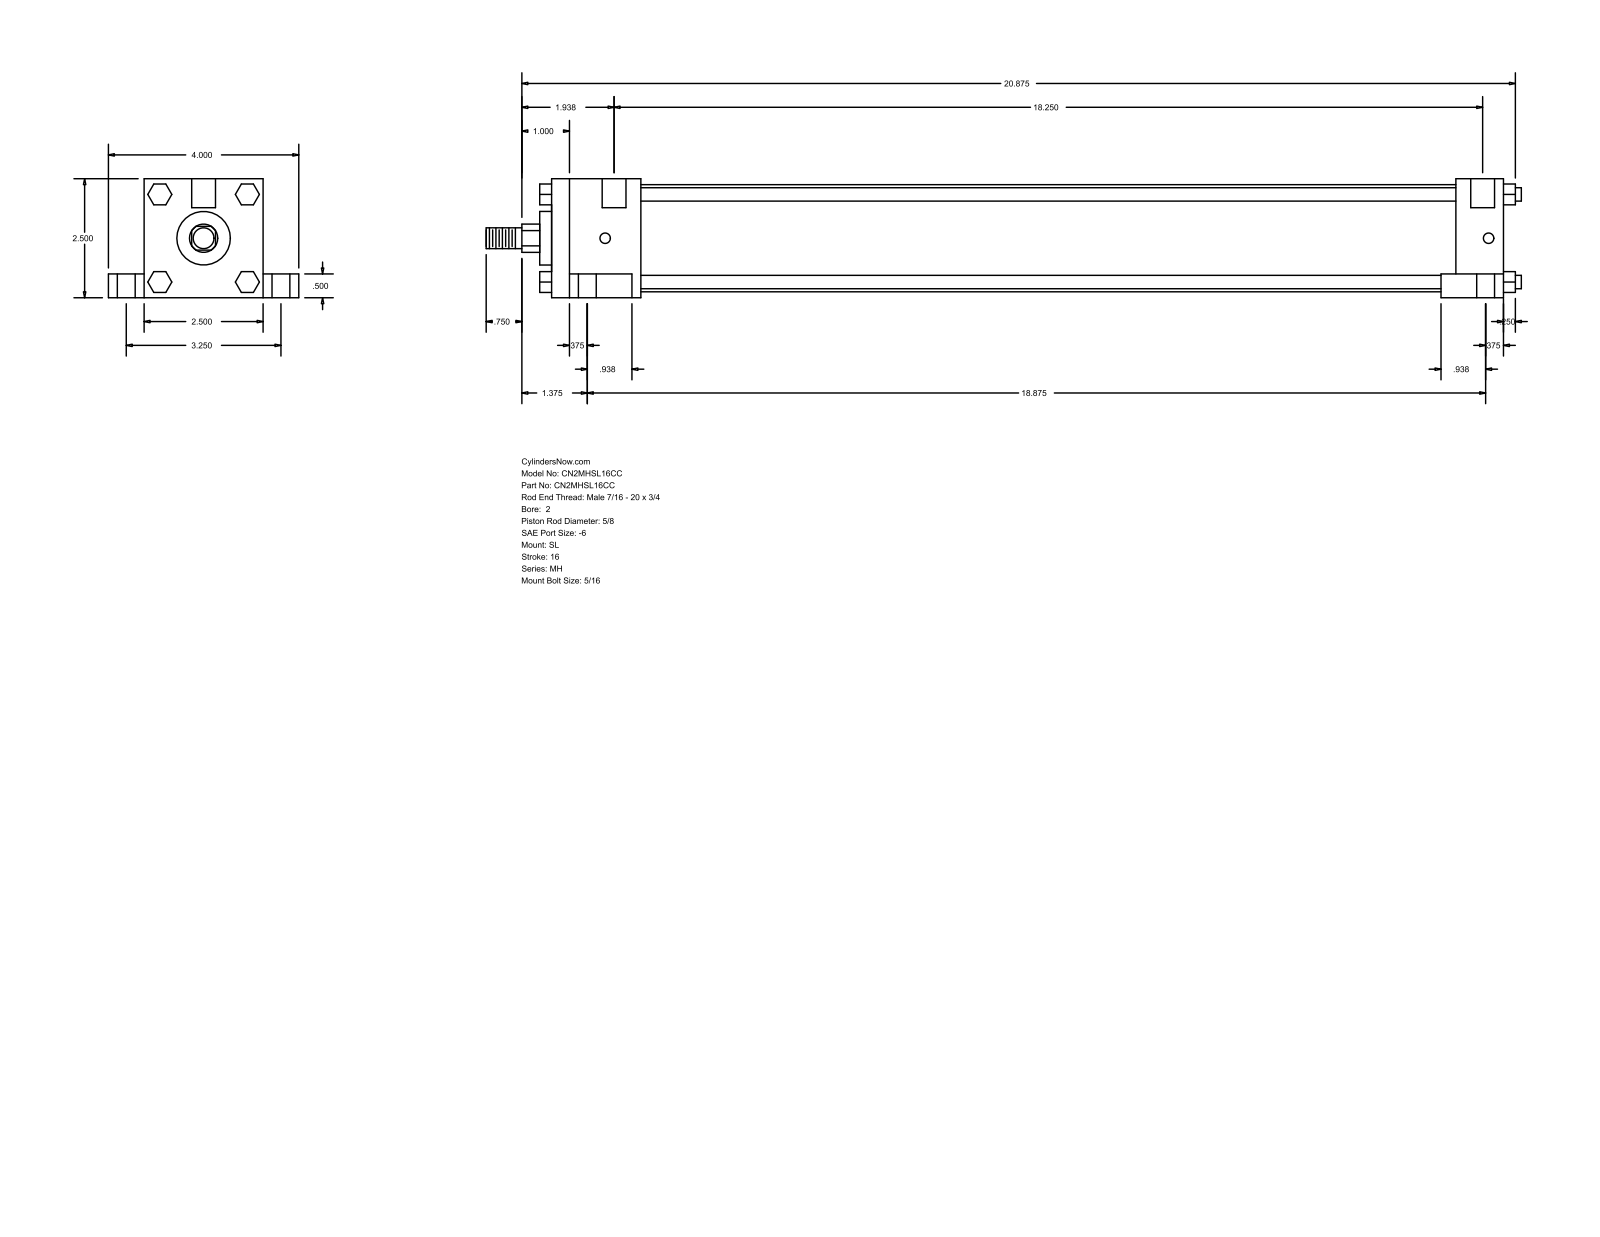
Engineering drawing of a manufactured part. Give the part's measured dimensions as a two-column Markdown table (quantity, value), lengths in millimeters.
| quantity | value |
| --- | --- |
| part name | MH_SL__0200_0.625 |
| STEP written by | GSSL Pune (CONFIG_CONTROL_DESIGN) |
| units | millimeters |
| bodies | 0 solids, 148 faces (112 planar, 36 cylindrical, 0 other) |
| overall size | 552.45 × 101.6 × 63.5 |
| round holes (diameter × count) | 5.56 × 4, 9.53 × 4, 15.88 × 4, 12.7 × 2 |
| round bosses / shafts (diameter × count) | 7.14 × 4, 57.15 × 1, 28.57 × 1, 15.88 × 1, 11.11 × 1 |
| partial cylindrical surfaces (radius × count) | 7.54 × 1 |
| main face-to-face distances | 63.5, 508, 12.7, 19.05, 82.55, 50.8, 25.4, 482.6, 47.62, 434.98 |
| hole center spacings | 41.3, 42.36, 43.67, 82.54, 466.97, 471.49, 471.71, 479.43 |
